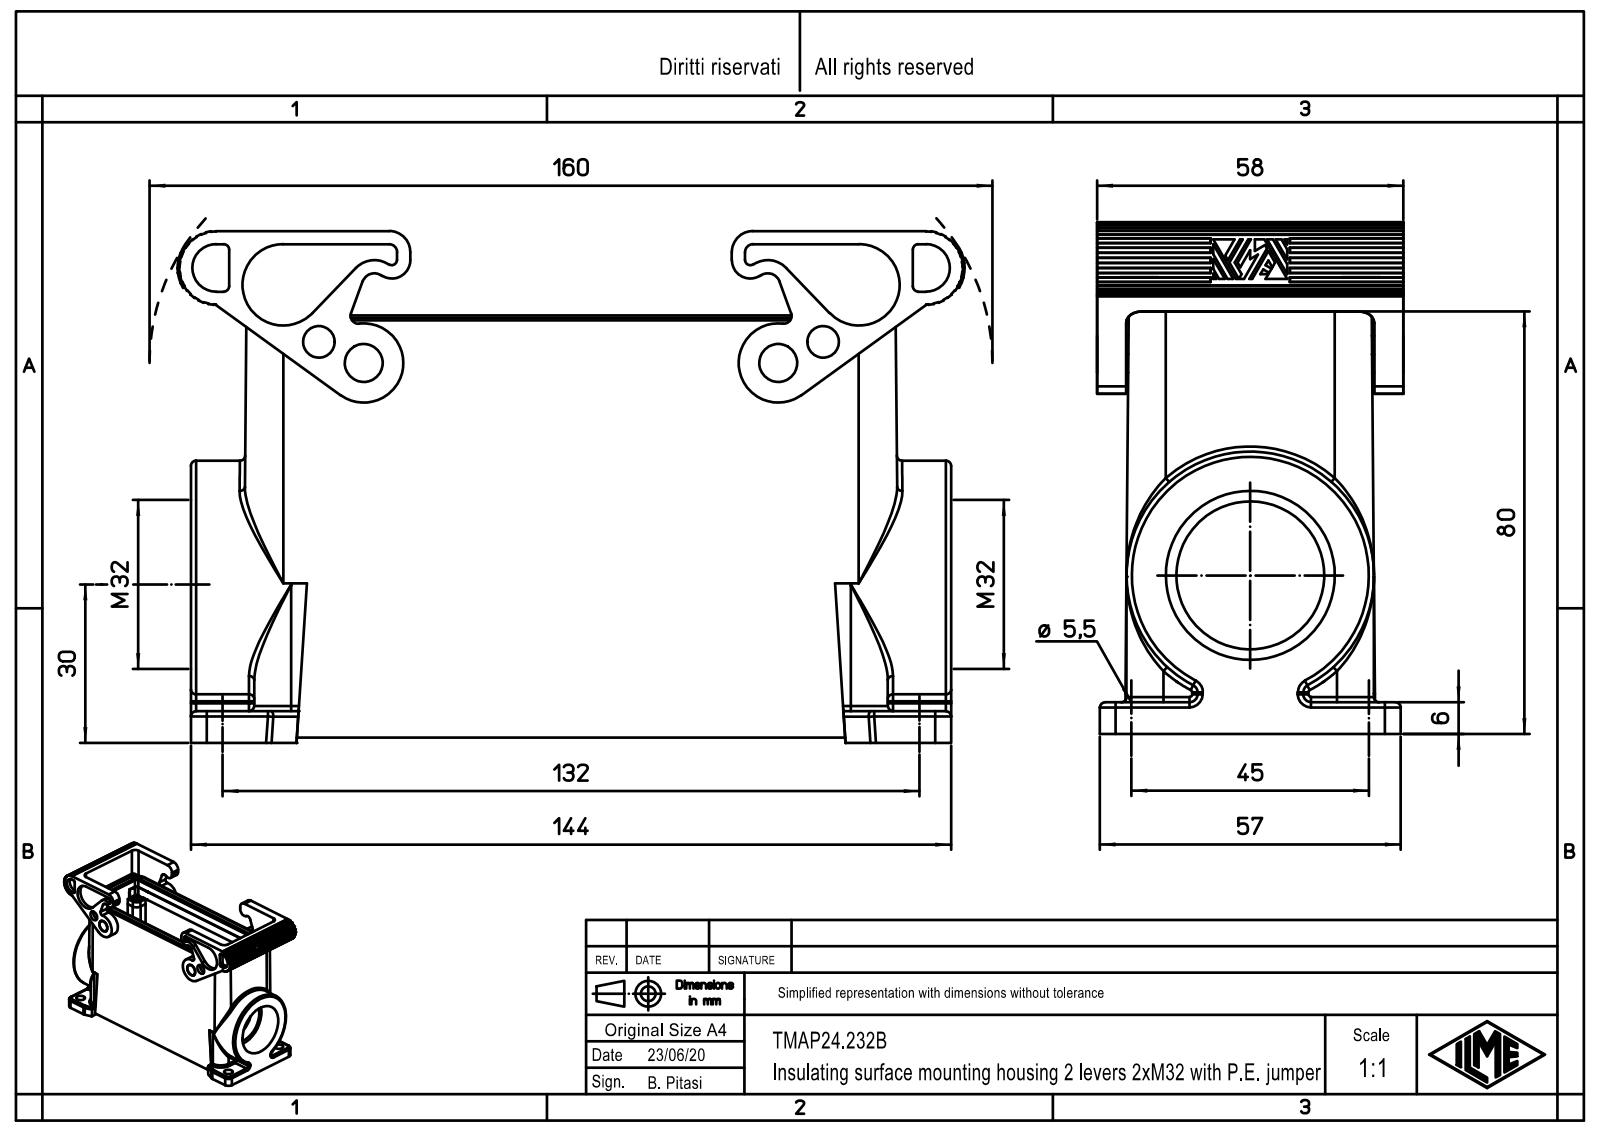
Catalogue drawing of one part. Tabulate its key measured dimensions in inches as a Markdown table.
| quantity | value |
| --- | --- |
| part name | TMAP24.232B |
| STEP written by | Creo Elements/Direct Modeling 20.1B 02-Apr-2019 (C) Parametric Technology GmbH (AUTOMOTIVE_DESIGN) |
| units | inches |
| bodies | 1 solid, 963 faces (549 planar, 282 cylindrical, 132 other) |
| overall size | 5.87 × 3.815 × 2.283 |
| volume | 14.33 in³ |
| surface area | 134.1 in² |
| round holes (diameter × count) | 0.118 × 4, 0.138 × 4, 0.217 × 4, 0.236 × 2, 0.394 × 2, 1.102 × 1, 1.26 × 1 |
| round bosses / shafts (diameter × count) | 0.189 × 4, 0.276 × 2, 1.845 × 1 |
| partial cylindrical surfaces (radius × count) | 0.039 × 22, 0.059 × 20, 0.118 × 12, 0.138 × 6, 0.276 × 6, 0.02 × 4, 0.051 × 4, 0.063 × 4 |
| main face-to-face distances | 1.598, 1.598, 0.217, 0.256, 0.039, 2.067, 4.315, 0.098, 2.185, 1.591 |
| hole center spacings | 0.655, 1.521, 4.659, 4.857, 0.37, 1.063, 1.772, 3.429 |
